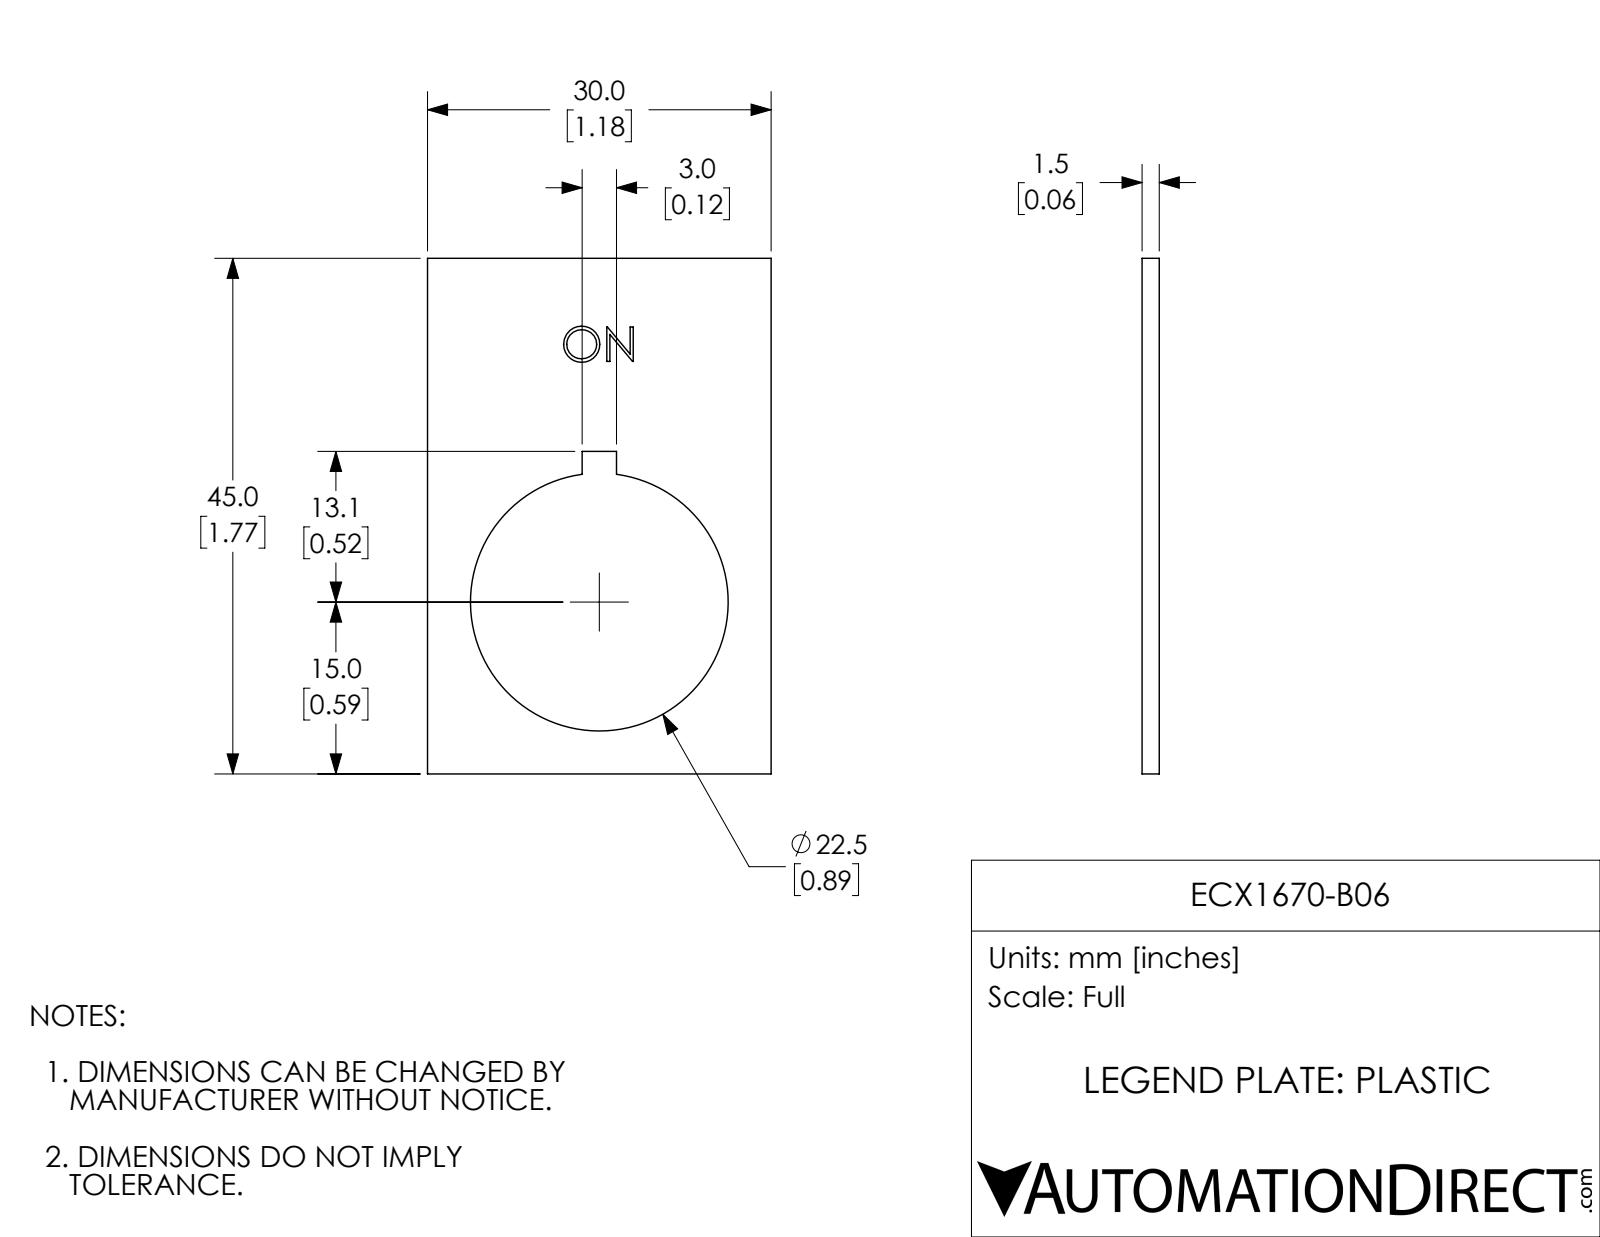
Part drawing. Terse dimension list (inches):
name: ECX1670-B06
written by: SolidWorks 2017 (AUTOMOTIVE_DESIGN)
unit: in
bodies: 1 solid, 33 faces (22 planar, 3 cylindrical, 8 other)
size: 1.772 × 1.181 × 0.059
volume: 0.087 in³; area: 3.458 in²
holes: 1× ⌀0.886
face distances: 0.059, 1.181, 1.772, 0.531, 0.65, 0.058, 1.108, 0.663, 0.118, 0.08
